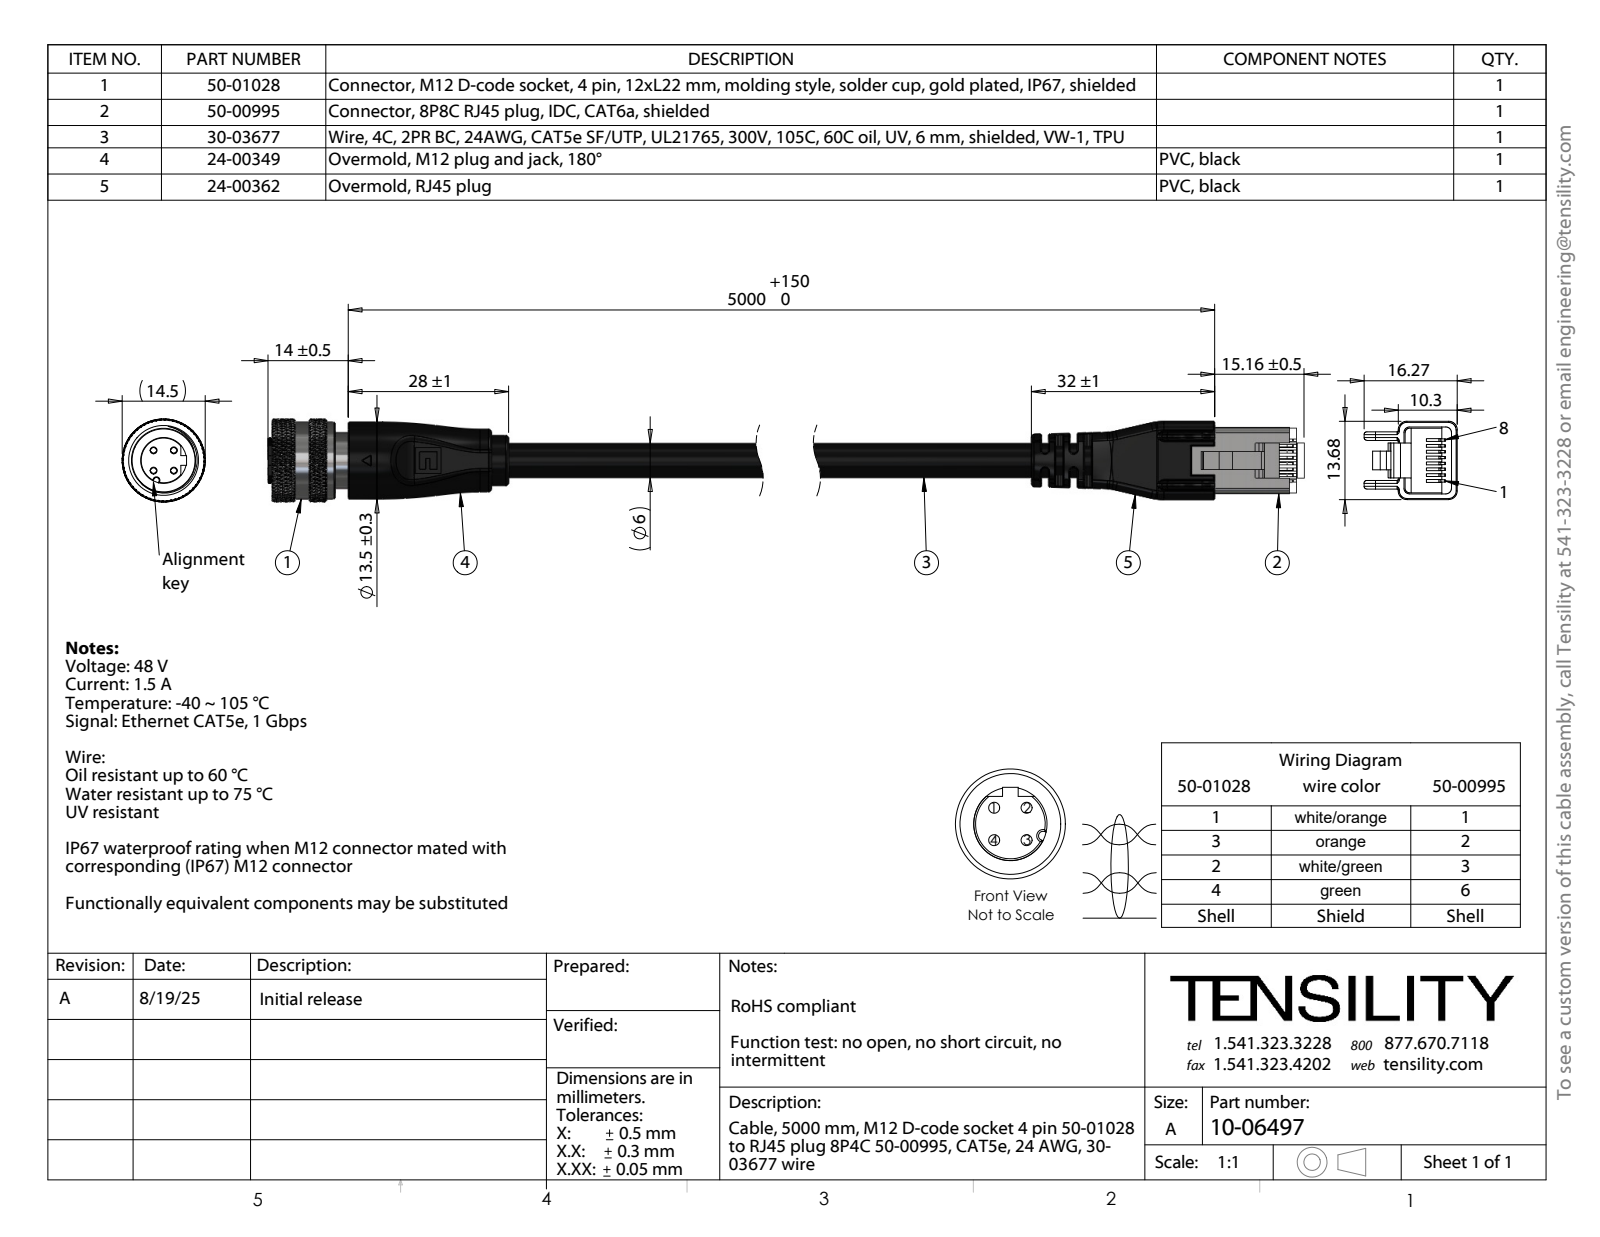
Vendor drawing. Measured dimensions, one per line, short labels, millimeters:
name: 50-01028-02_默认; 50-01028-04_默认; 50-01028-01_默认; 50-01028-05_默认 (+7 more)
written by: SolidWorks 2025 (CONFIG_CONTROL_DESIGN)
unit: mm
bodies: 55 solids, 3967 faces (546 planar, 928 cylindrical, 2493 other)
size: 229.11 × 18.37 × 14.5
volume: 14 248 mm³; area: 29 704 mm²
holes: 28× ⌀0.2, 4× ⌀1.05, 4× ⌀1.1, 4× ⌀1.2, 1× ⌀3.16, 1× ⌀3.21, 1× ⌀3.56, 1× ⌀9, 1× ⌀10, 1× ⌀11.2
bosses: 4× ⌀1.6, 4× ⌀1.5, 1× ⌀13.5, 1× ⌀11, 1× ⌀10.6, 1× ⌀10.5, 1× ⌀9.8, 1× ⌀9.7
rounds: 11× R0.2, 10× R0.1, 10× R0.5, 10× R1.5, 8× R0.62, 6× R0.4, 5× R1, 4× R10
face distances: 1.25, 1, 2.5, 3.75, 9.3, 5, 1.5, 199.5, 12.68, 8.5
hole spacings: 1.91, 0.36, 2.09, 1.06, 0.89, 1.08, 1.24, 1.8
